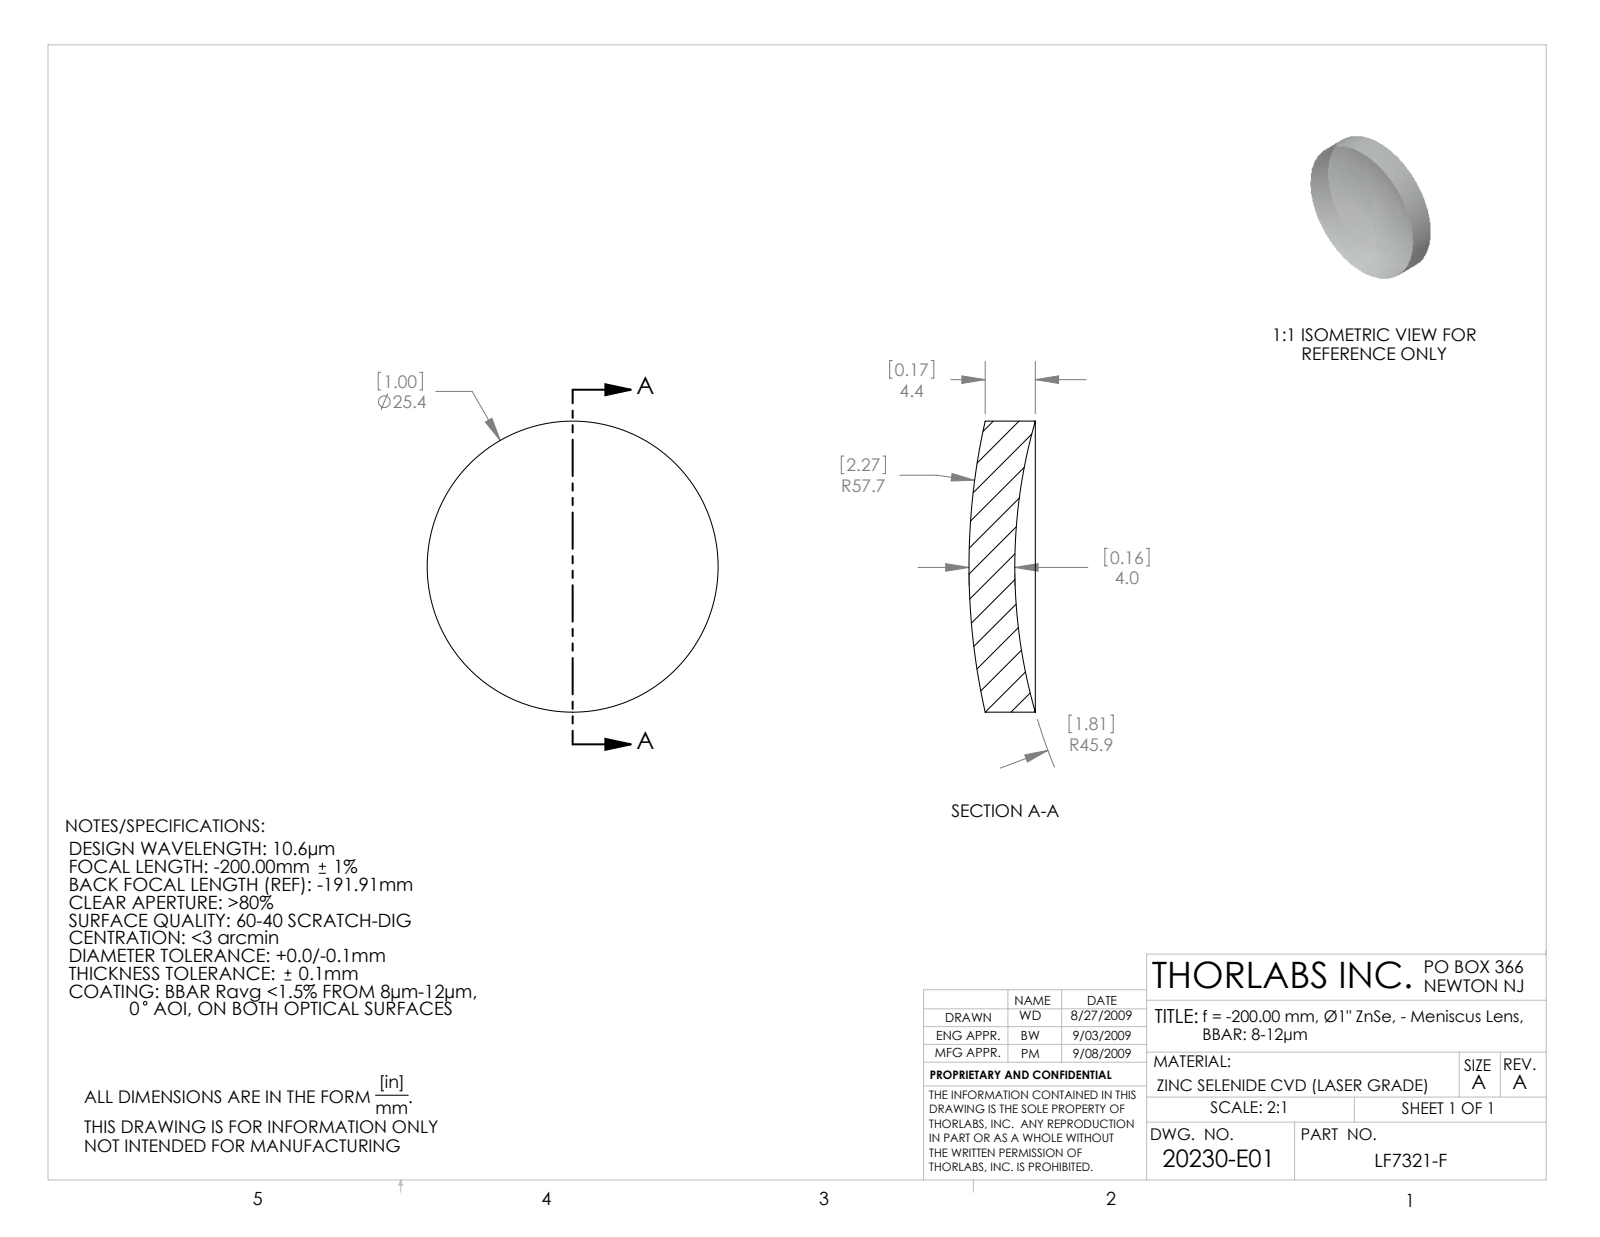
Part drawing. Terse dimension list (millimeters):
name: 20230-E0W
written by: SolidWorks 2007 (CONFIG_CONTROL_DESIGN)
unit: mm
bodies: 1 solid, 6 faces (0 planar, 2 cylindrical, 4 other)
size: 25.4 × 25.4 × 5.79
volume: 2 121 mm³; area: 1 379 mm²
bosses: 1× ⌀25.4
